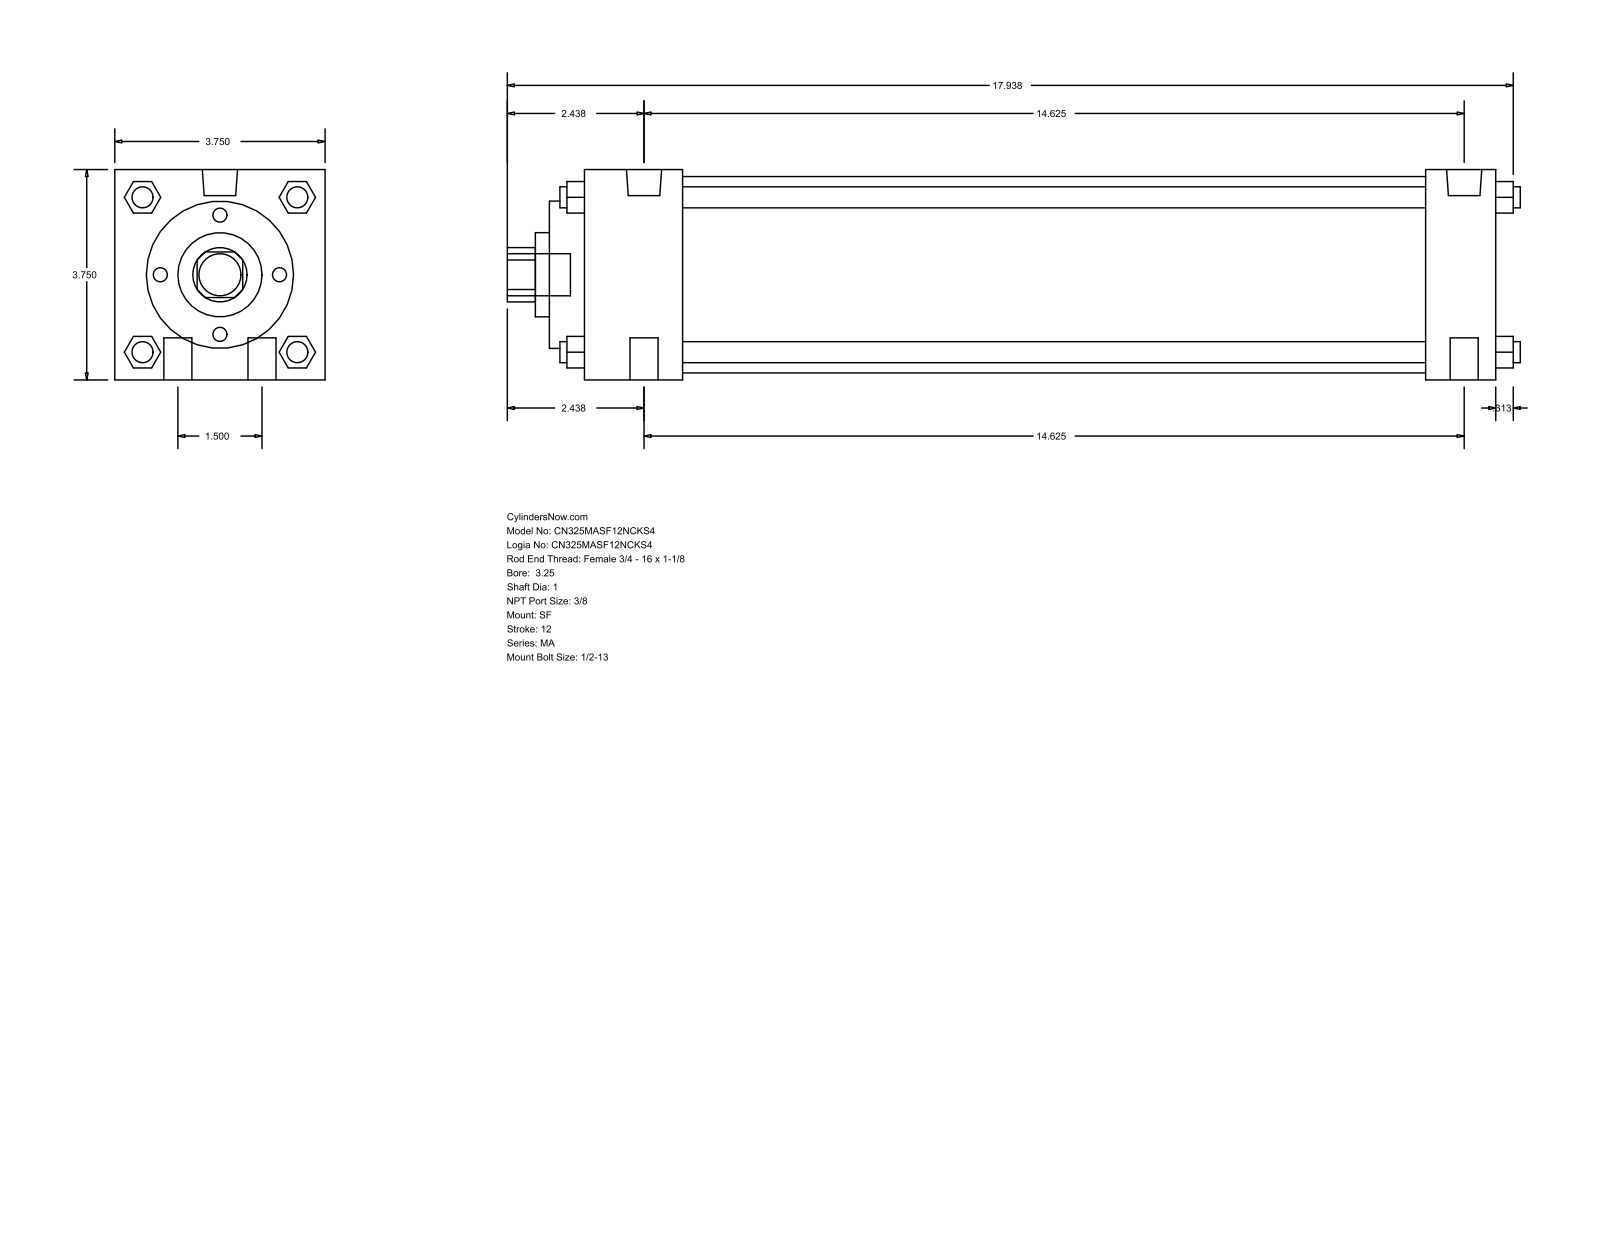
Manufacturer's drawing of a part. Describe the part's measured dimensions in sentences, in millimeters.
The part is named "MA_SF__0325_1". Its 3-D file was written by "GSSL Pune (CONFIG_CONTROL_DESIGN)". It is 0 solids with 126 faces: 95 planar, 31 cylindrical and 0 other. Overall it measures 458.79 by 95.25 by 95.25 millimeters. Round holes: 1 of diameter 25.4, 1 of diameter 38.1, 1 of diameter 66.67, 1 of diameter 88.9. Round bosses or shafts: 4 of diameter 12.7, 4 of diameter 9.53, 2 of diameter 15.93, 2 of diameter 11.11, 1 of diameter 19.05. Partial cylindrical surfaces (rounded edges, fillets, slot ends): 1 of radius 12.29. The main face-to-face distances are 95.24, 412.76, 15.87, 381.01, 31.75, 44.46, 336.55, 368.3, 60.33, 396.88.
